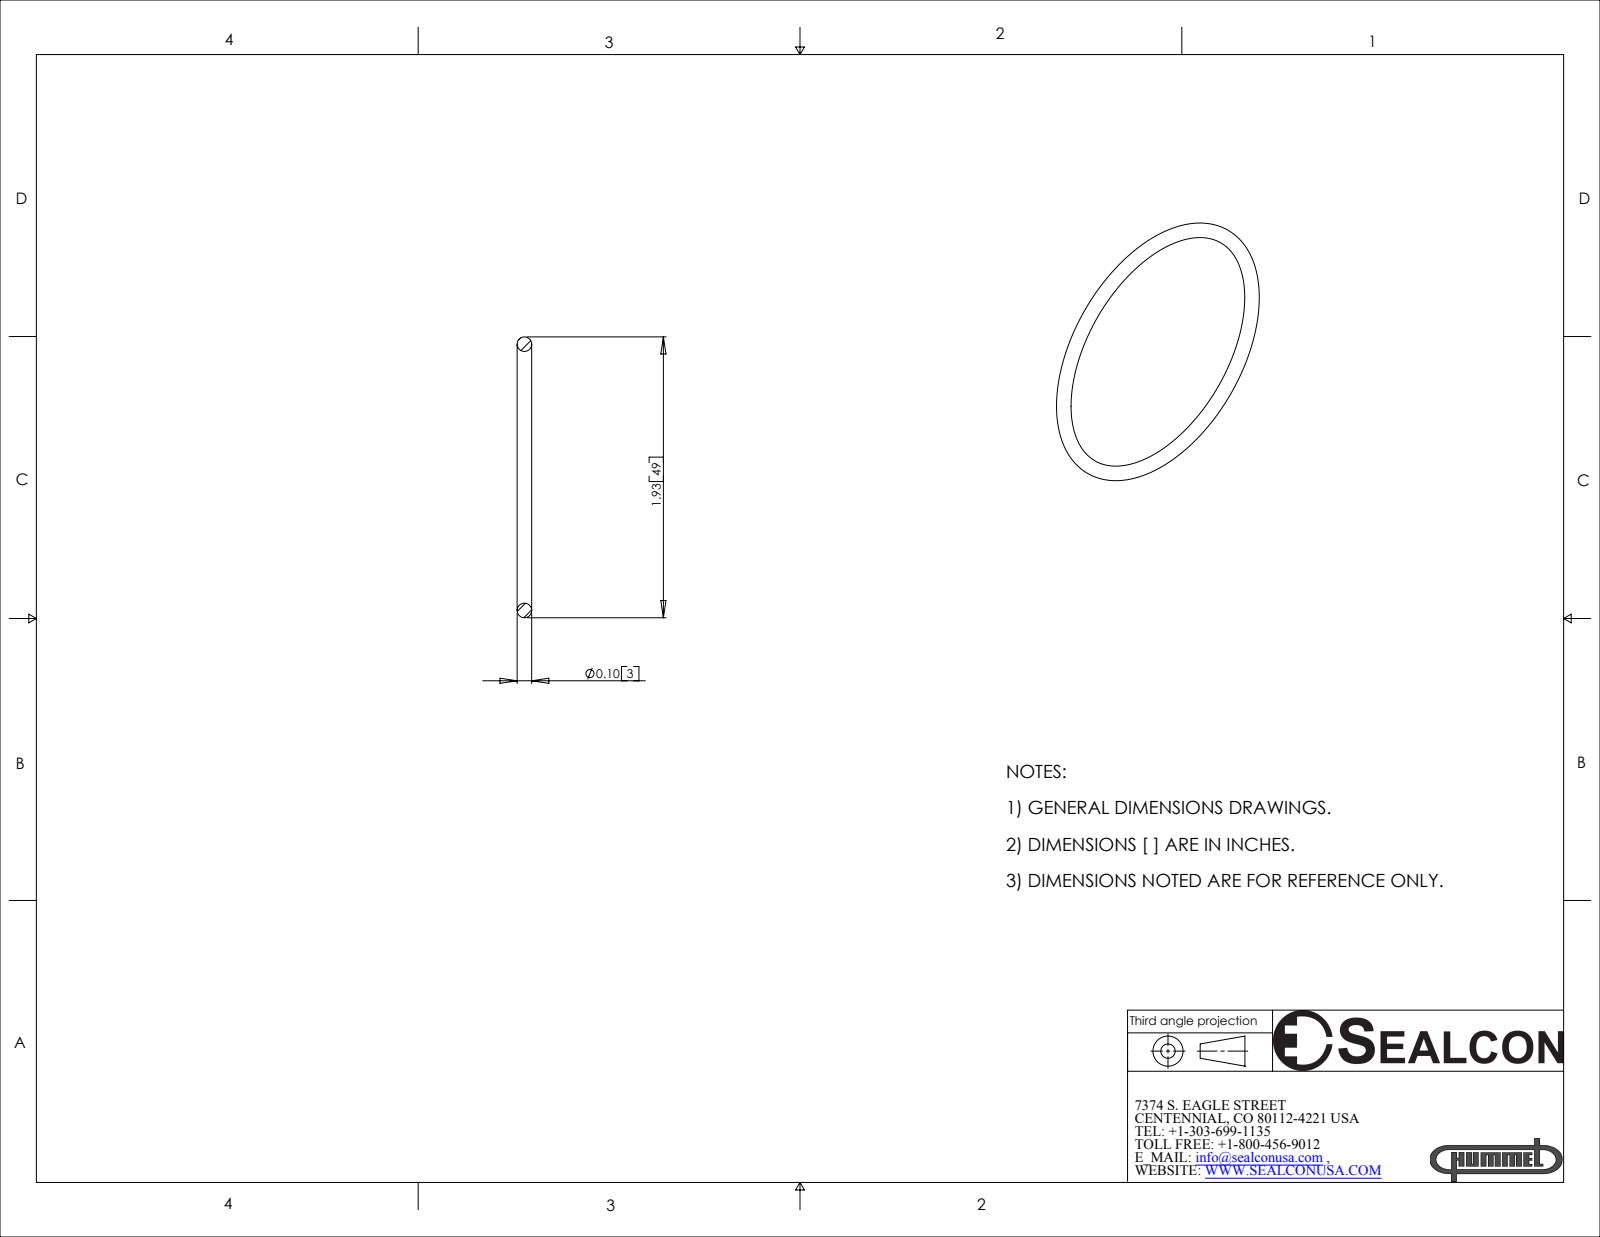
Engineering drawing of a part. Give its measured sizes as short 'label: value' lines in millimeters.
name: OR-36-VT
written by: SolidWorks 2007 (CONFIG_CONTROL_DESIGN)
unit: mm
bodies: 1 solid, 4 faces (0 planar, 0 cylindrical, 4 other)
size: 49 × 49 × 2.5
volume: 740 mm³; area: 1 165 mm²
